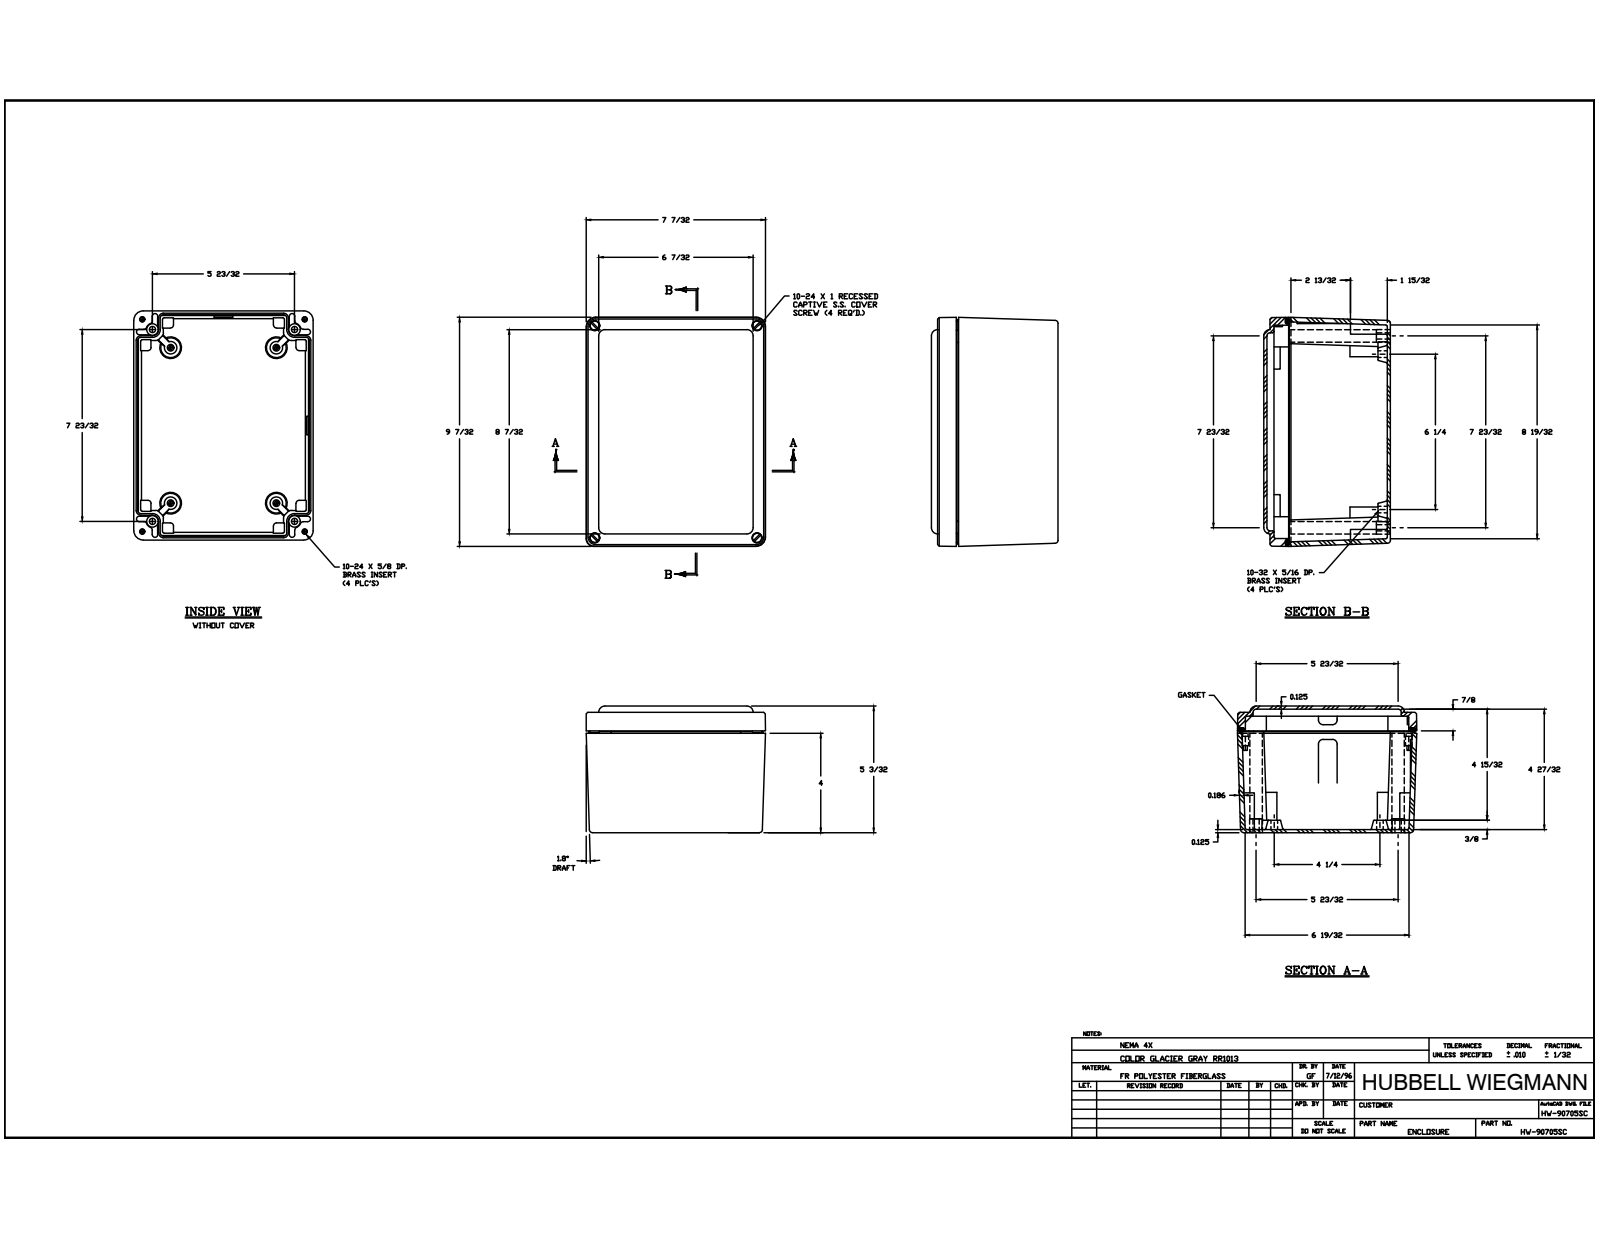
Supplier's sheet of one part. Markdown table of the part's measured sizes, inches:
| quantity | value |
| --- | --- |
| part name | WP907WBOX; 0.3125-18 X 0.563 DP BRASS INSERT; 10-32 X0.3125 DP BRASS INSERT; 10-24 X 0.625 DP BRASS INSERT (+5 more) |
| STEP written by | Autodesk Inventor 2014 (AUTOMOTIVE_DESIGN) |
| units | inches |
| bodies | 23 solids, 1100 faces (436 planar, 296 cylindrical, 368 other) |
| overall size | 9.22 × 7.22 × 5.094 |
| volume | 57.17 in³ |
| surface area | 647.9 in² |
| round holes (diameter × count) | 0.281 × 8, 0.145 × 4, 0.156 × 4, 0.156 × 4, 0.19 × 4, 0.219 × 4, 0.23 × 4, 0.28 × 4, 0.313 × 4, 0.406 × 4, 0.531 × 4 |
| round bosses / shafts (diameter × count) | 0.375 × 4, 0.364 × 4, 0.191 × 4 |
| partial cylindrical surfaces (radius × count) | 0.031 × 57, 0.125 × 38, 0.063 × 29, 0.01 × 16, 0.059 × 8, 0.188 × 8, 0.25 × 8, 0.375 × 8 |
| main face-to-face distances | 0.186, 0.125, 4.844, 5.094, 4.969, 0.125, 4.969, 4.094, 0.75, 0.25 |
| hole center spacings | 0.574, 0.574, 1.039, 1.613, 1.613, 5.04, 5.511, 5.511 |
